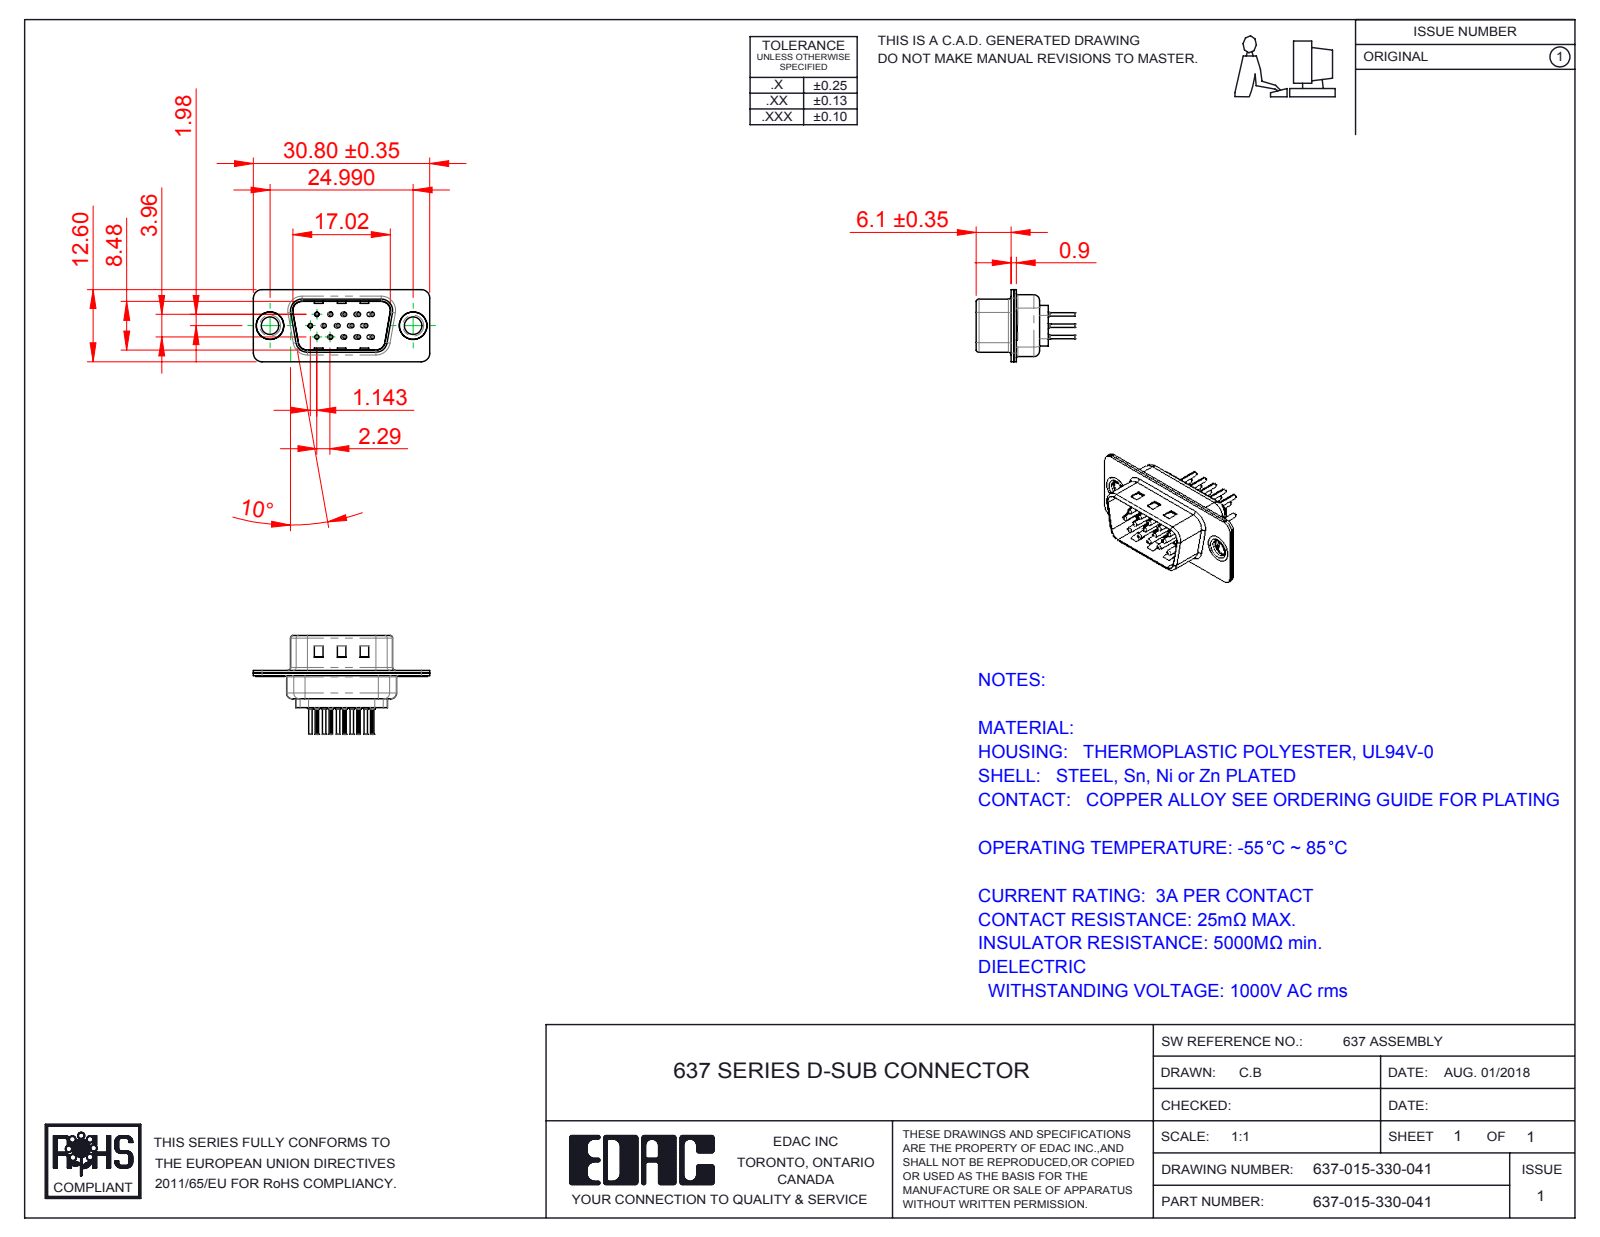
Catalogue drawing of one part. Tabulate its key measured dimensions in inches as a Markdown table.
| quantity | value |
| --- | --- |
| part name | 637 Contact Row 1_30; 637 Contact Row 3_30; 637 Thru Hole Rivet; 637 Housing_15 Contacts (+4 more) |
| STEP written by | SolidWorks 2016 (CONFIG_CONTROL_DESIGN) |
| units | inches |
| bodies | 20 solids, 1778 faces (467 planar, 668 cylindrical, 643 other) |
| overall size | 1.213 × 0.679 × 0.496 |
| volume | 0.076 in³ |
| surface area | 6.977 in² |
| round holes (diameter × count) | 0.063 × 27, 0.008 × 15, 0.014 × 15, 0.043 × 15, 0.03 × 12, 0.079 × 12, 0.12 × 2, 0.157 × 2, 0.189 × 2 |
| round bosses / shafts (diameter × count) | 0.079 × 15, 0.059 × 15, 0.03 × 15, 0.024 × 15, 0.197 × 2, 0.193 × 2, 0.14 × 2 |
| partial cylindrical surfaces (radius × count) | 0.004 × 30, 0.059 × 16, 0.079 × 12, 0.02 × 8, 0.01 × 4, 0.022 × 4, 0.028 × 4, 0.037 × 4 |
| main face-to-face distances | 0.018, 0.035, 0.016, 0.334, 0.028, 0.35, 0.041, 0.012, 0.179, 0.046 |
| hole center spacings | 0.156, 0.09, 0.09, 0.18, 0.095, 0.238, 0.191, 0.093 |
